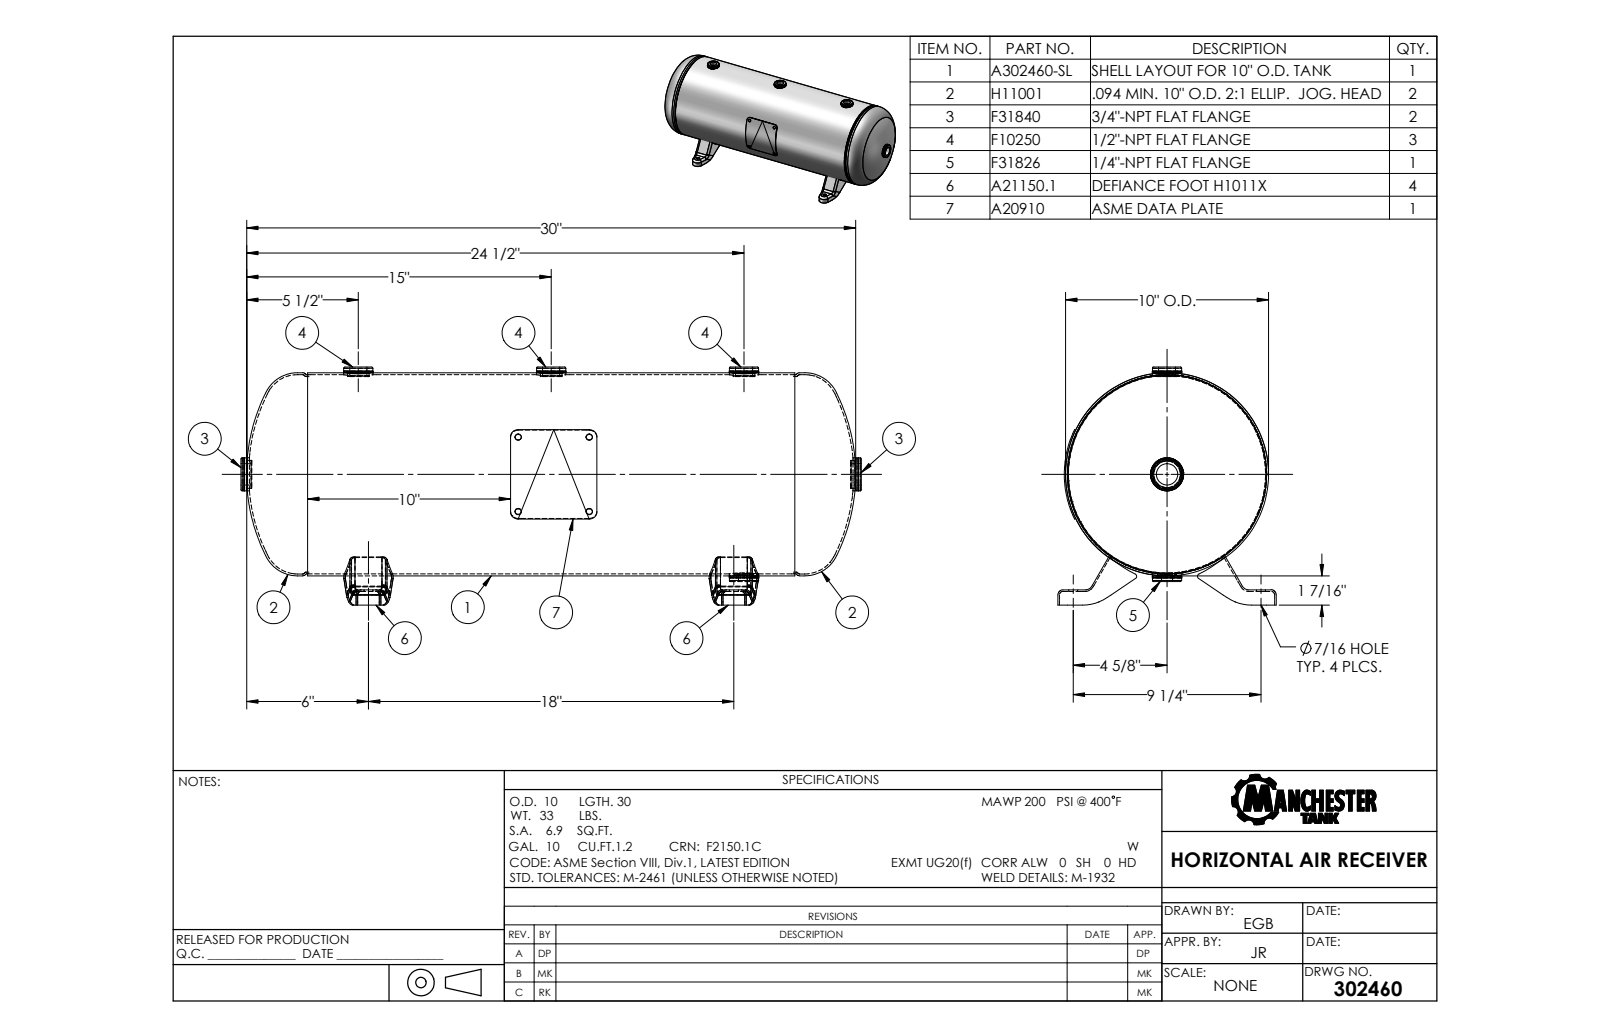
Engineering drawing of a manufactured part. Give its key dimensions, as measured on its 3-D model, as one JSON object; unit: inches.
{"part_name": "302460", "step_written_by": "SolidWorks 2011 (CONFIG_CONTROL_DESIGN)", "units": "inches", "bodies": {"solids": 0, "faces": 331, "planar": 79, "cylindrical": 102, "other": 150}, "overall_size": [31.188, 11.925, 10.75], "round_holes": [[0.437, 4], [0.84, 3], [0.54, 1], [1, 1], [1.05, 1]], "round_bosses_or_shafts": [[1.813, 3], [10, 1], [2.062, 1], [1.5, 1], [1.438, 1], [1.188, 1]], "partial_cylinders_radius": [[0.25, 10], [0.16, 8], [0.41, 4], [0.5, 4], [0.125, 2], [0.34, 2], [1.209, 2], [5.06, 1]], "face_to_face_distances": [0.09, 17.406, 3.387, 24.25, 3.476, 20.793, 17.317, 17.496, 5.81, 5.72], "hole_center_spacings": [4.652, 10.119, 19.069, 9.25, 9.5, 18, 20.237, 19]}
